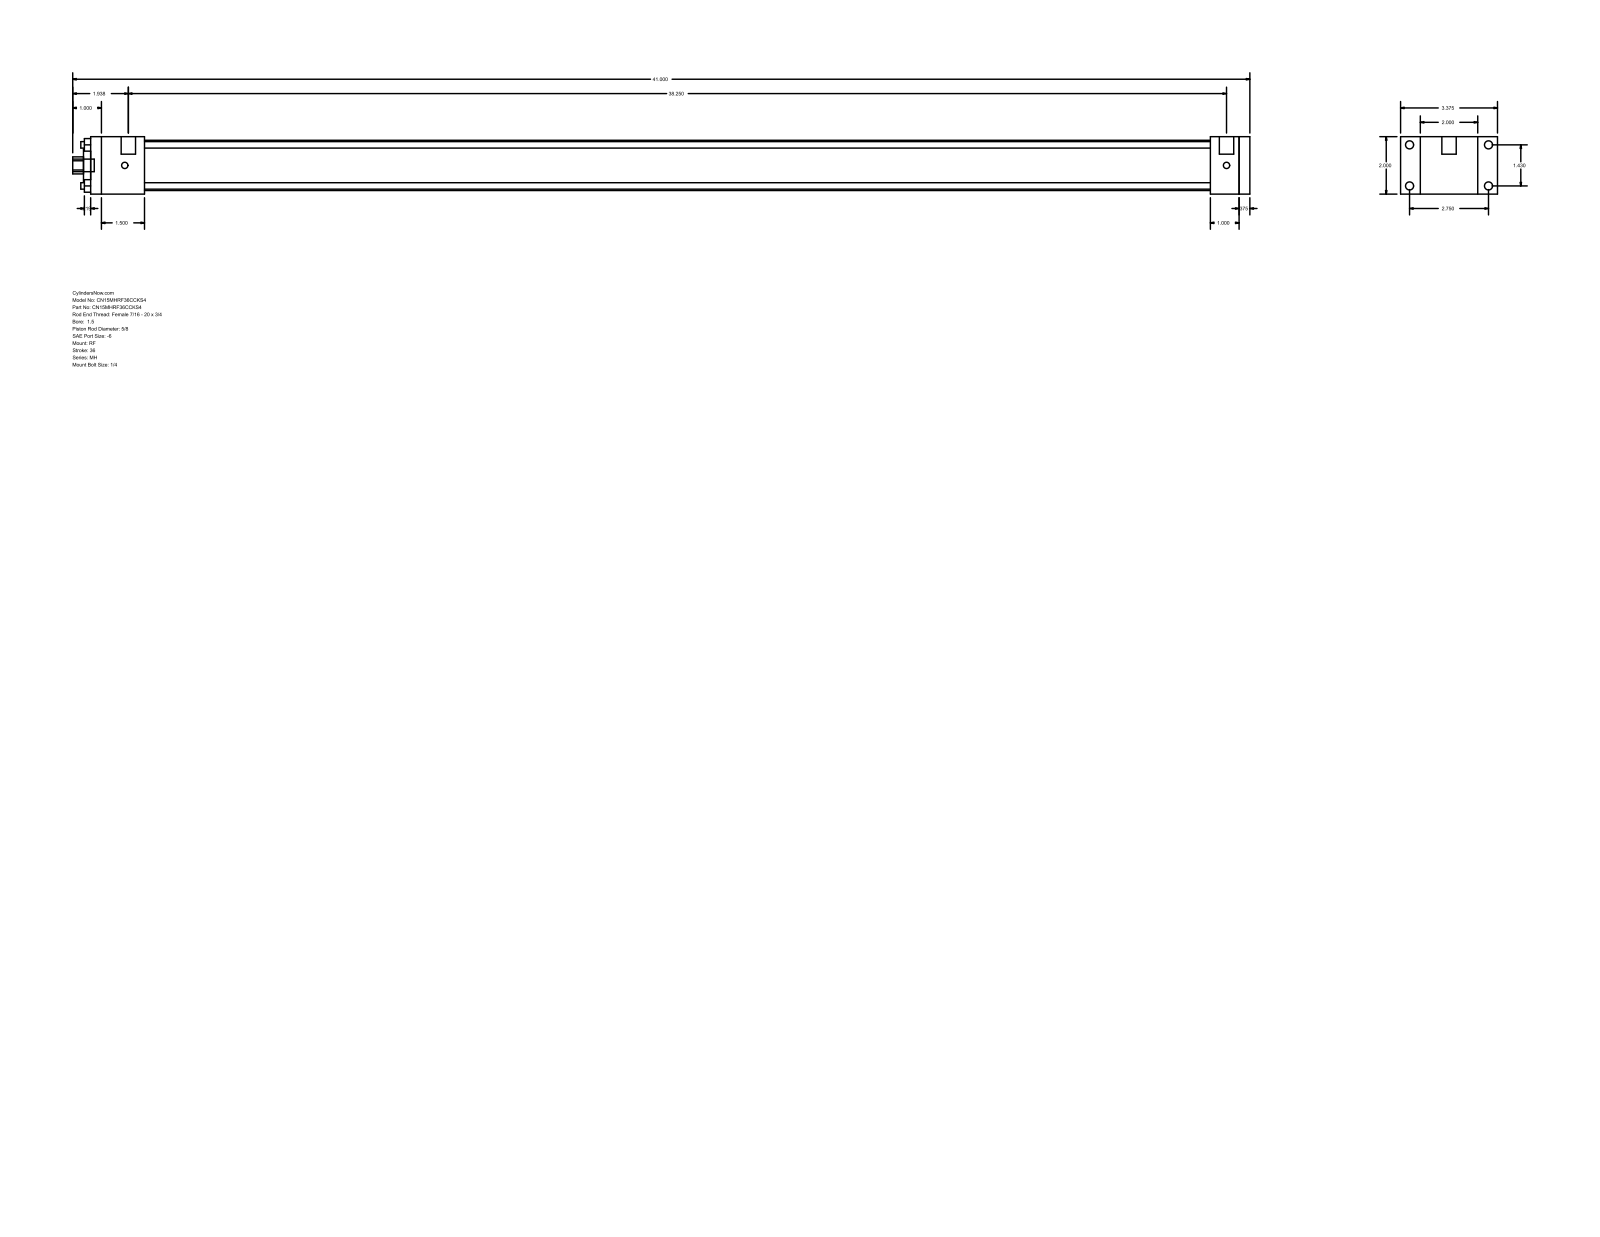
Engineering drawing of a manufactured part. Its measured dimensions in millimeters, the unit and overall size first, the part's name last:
Units: millimetres
Overall size (bounding box): 1041.4 × 85.72 × 50.8
Round holes (diameter × count): ⌀5.71 ×4, ⌀15.88 ×1, ⌀28.57 ×1, ⌀44.45 ×1
Round bosses / shafts (diameter × count): ⌀7.14 ×4, ⌀5.56 ×4, ⌀12.7 ×2, ⌀11.11 ×1
Partial cylindrical surfaces — rounded edges, fillets, slot ends (radius × count): R7.54 ×1
Main face-to-face distances: 50.8, 9.52, 1016, 1025.52, 17.46, 68.26, 990.6, 25.4, 34.92, 47.62
Hole centre spacings: 25.68, 36.32, 51.36
Bodies: 0 solids, 92 faces (64 planar, 28 cylindrical, 0 other)
Part name (STEP PRODUCT): MH_RF__0150_0.625
STEP written by: GSSL Pune (CONFIG_CONTROL_DESIGN)
